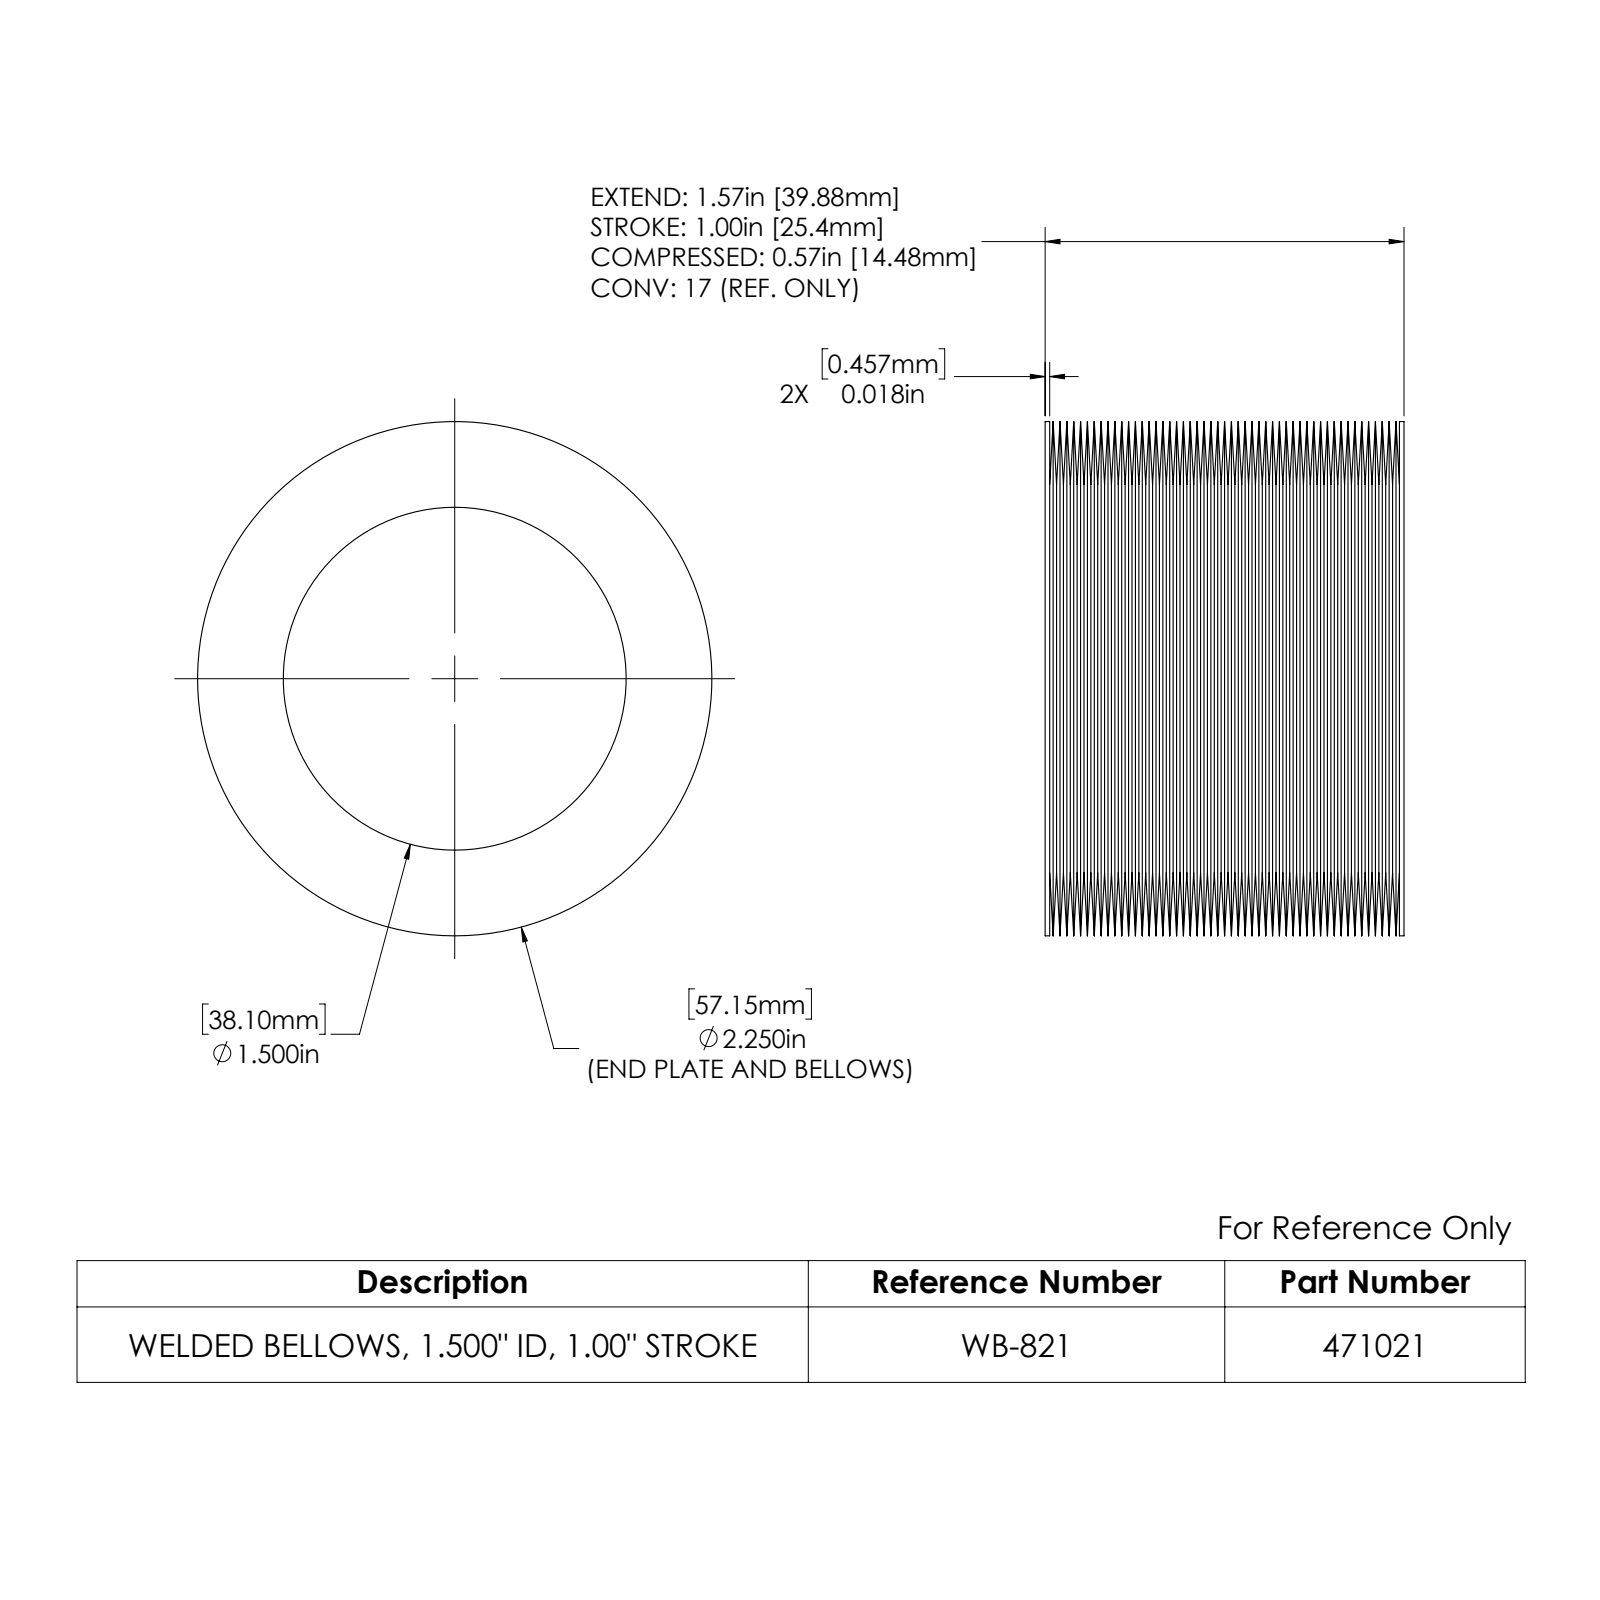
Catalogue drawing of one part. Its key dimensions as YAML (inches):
part_name: "471021"
step_written_by: "SolidWorks 2022 (CONFIG_CONTROL_DESIGN)"
units: inches
bodies: {solids: 1, faces: 214, planar: 4, cylindrical: 6, other: 204}
overall_size: [2.25, 2.25, 1.57]
volume: 2.102
surface_area: 189.8
round_holes:
  - {diameter: 1.5, count: 1}
round_bosses_or_shafts:
  - {diameter: 2.25, count: 1}
face_to_face_distances: [0.02, 1.55, 1.57, 1.53]
